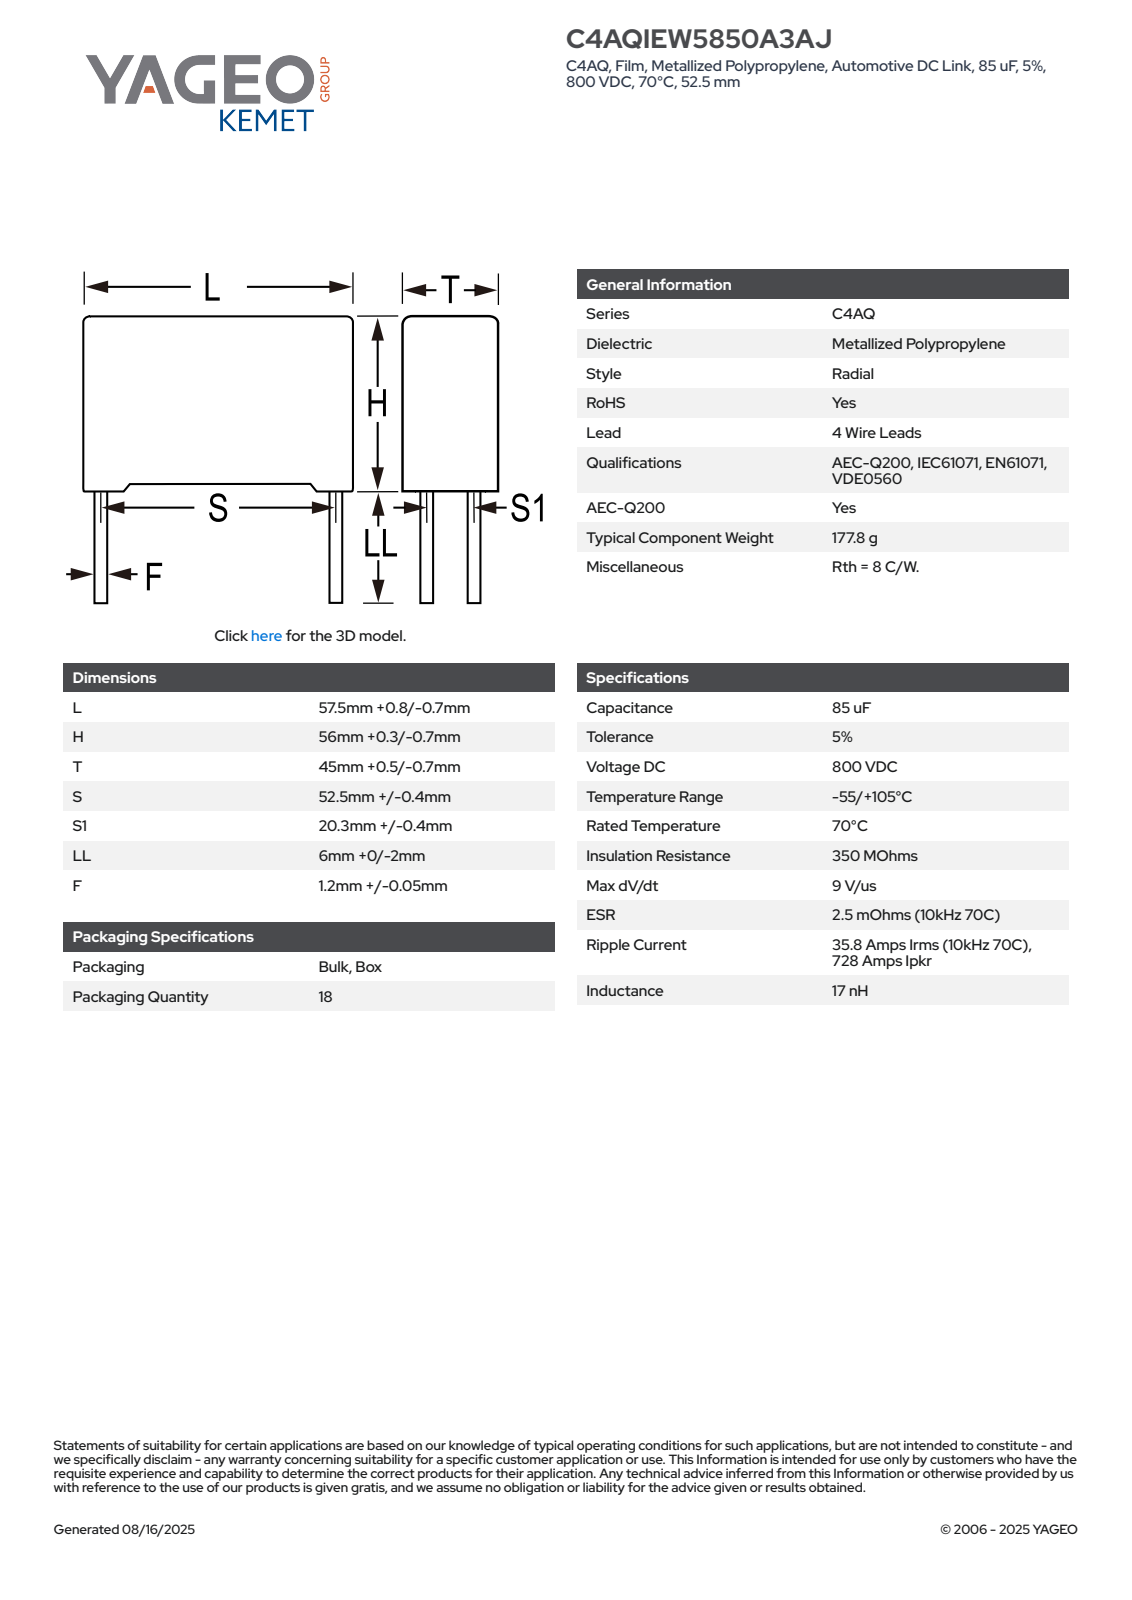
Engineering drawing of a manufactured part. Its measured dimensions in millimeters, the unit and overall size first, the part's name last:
Units: millimetres
Overall size (bounding box): 62.3 × 58.3 × 45.51
Round bosses / shafts (diameter × count): ⌀1.25 ×4
Main face-to-face distances: 45.5, 58.3, 54.64, 1.66, 56.3, 2.8, 55.5, 52.7, 42.7, 39.9
Volume: 145 501 mm³ · Surface area: 17 347 mm²
Bodies: 4 solids, 91 faces (83 planar, 8 cylindrical, 0 other)
Part name (STEP PRODUCT): CFP_RB4_57.5X56X45_L58.3H56.3T45.5S52.5S120.3LL6F1.25
STEP written by: SolidWorks 2021 (AUTOMOTIVE_DESIGN)
